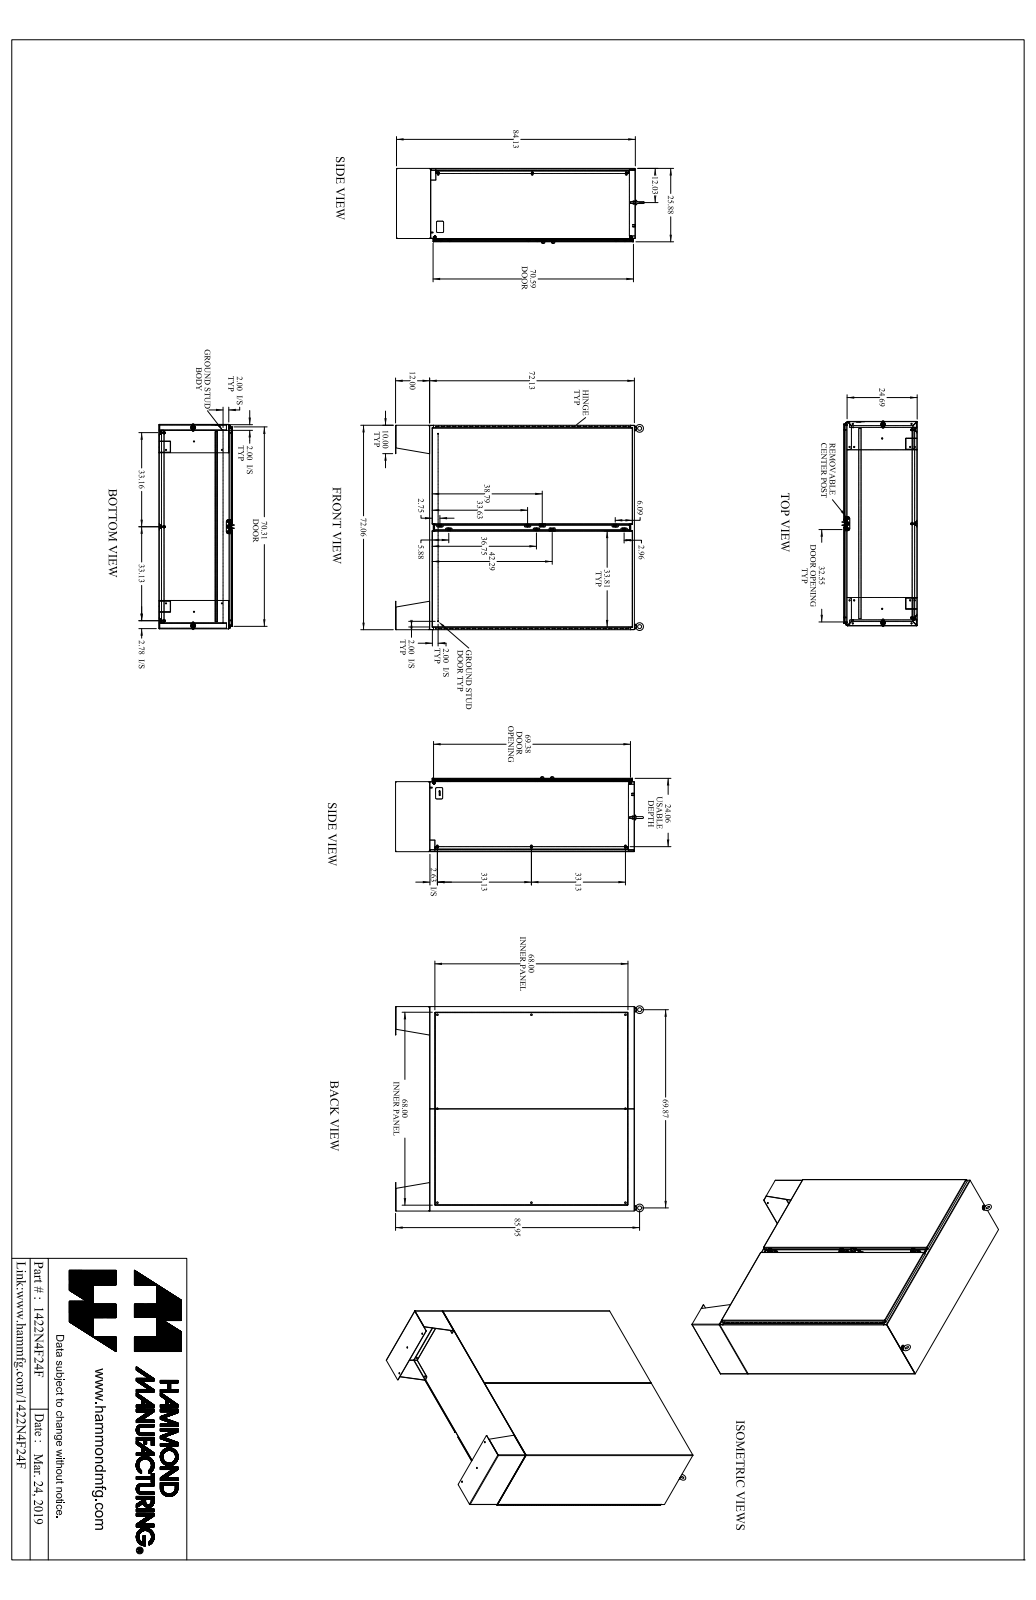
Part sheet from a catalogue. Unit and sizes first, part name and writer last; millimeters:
Units: millimetres
Overall size (bounding box): 2229.6 × 1857.3 × 672.3
Round holes (diameter × count): ⌀7.7 ×24, ⌀11.1 ×14, ⌀7.8 ×8, ⌀14.3 ×8, ⌀5.4 ×6, ⌀6.7 ×6, ⌀11.3 ×6, ⌀5.1 ×3, ⌀6.4 ×3, ⌀8 ×3, ⌀9.5 ×3, ⌀9.5 ×3
Round bosses / shafts (diameter × count): ⌀25.4 ×8, ⌀16.5 ×8, ⌀9.5 ×8, ⌀8.4 ×8, ⌀12.7 ×6, ⌀9.9 ×6, ⌀6.2 ×6, ⌀7.1 ×4
Partial cylindrical surfaces — rounded edges, fillets, slot ends (radius × count): R1.2 ×67, R3.6 ×67, R6.4 ×34, R1.5 ×18, R4.7 ×14, R2.9 ×12, R3.6 ×12, R4.7 ×12
Main face-to-face distances: 2.4, 3.2, 654.8, 651.6, 3.2, 654.1, 657.2, 608.8, 42.8, 611.2
Hole centre spacings: 152.4, 1789.7, 304.8, 1809.1, 457.2, 1840.9, 609.6, 1884.5
Volume: 46 590 000 mm³ · Surface area: 34 990 000 mm²
Bodies: 109 solids, 3636 faces (1846 planar, 1578 cylindrical, 212 other)
Part name (STEP PRODUCT): 1422N4F24F_Default
STEP written by: SolidWorks 2019 (CONFIG_CONTROL_DESIGN)
